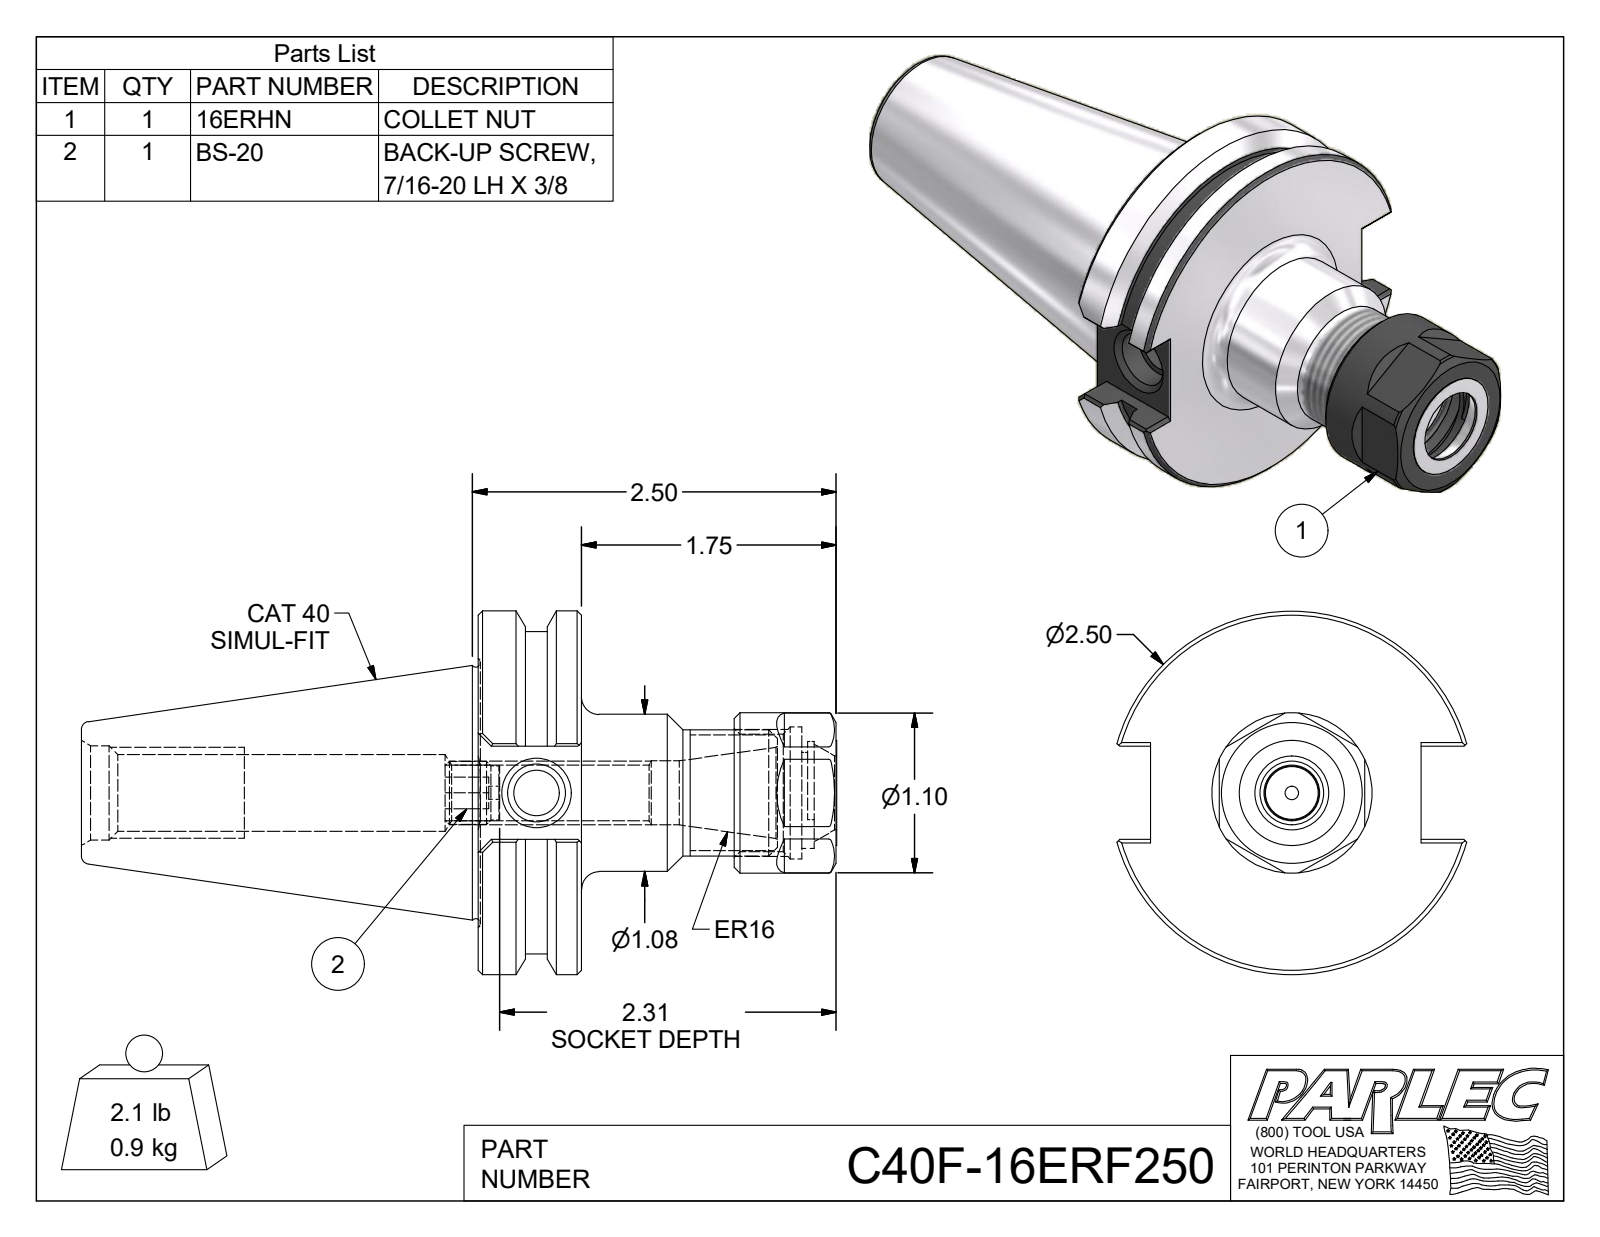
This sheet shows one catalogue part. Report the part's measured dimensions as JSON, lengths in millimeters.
{"part_name": "C40F-16ER2-1; 16ERHN; BS-20; C40F-16ERF250", "step_written_by": "Autodesk Inventor 2016 (AUTOMOTIVE_DESIGN)", "units": "millimeters", "bodies": {"solids": 3, "faces": 123, "planar": 57, "cylindrical": 24, "other": 42}, "overall_size": [131.76, 63.5, 61.11], "volume_mm3": 122782, "surface_area_mm2": 27966, "round_holes": [[2.29, 1], [8, 1], [9.73, 1], [10.13, 1], [11.18, 1], [12.4, 1], [13.39, 1], [16.46, 1], [17.02, 1], [20.5, 1], [23, 1]], "round_bosses_or_shafts": [[63.5, 1], [56.26, 1], [28, 1], [27.43, 1], [22, 1], [10.97, 1], [9.46, 1]], "partial_cylinders_radius": [[7.24, 1], [9, 1]], "face_to_face_distances": [18.04, 62.49, 44.45, 25.15, 56.79, 38.75, 5.7, 47.24, 16.26, 44.82], "hole_center_spacings": [1.52]}
